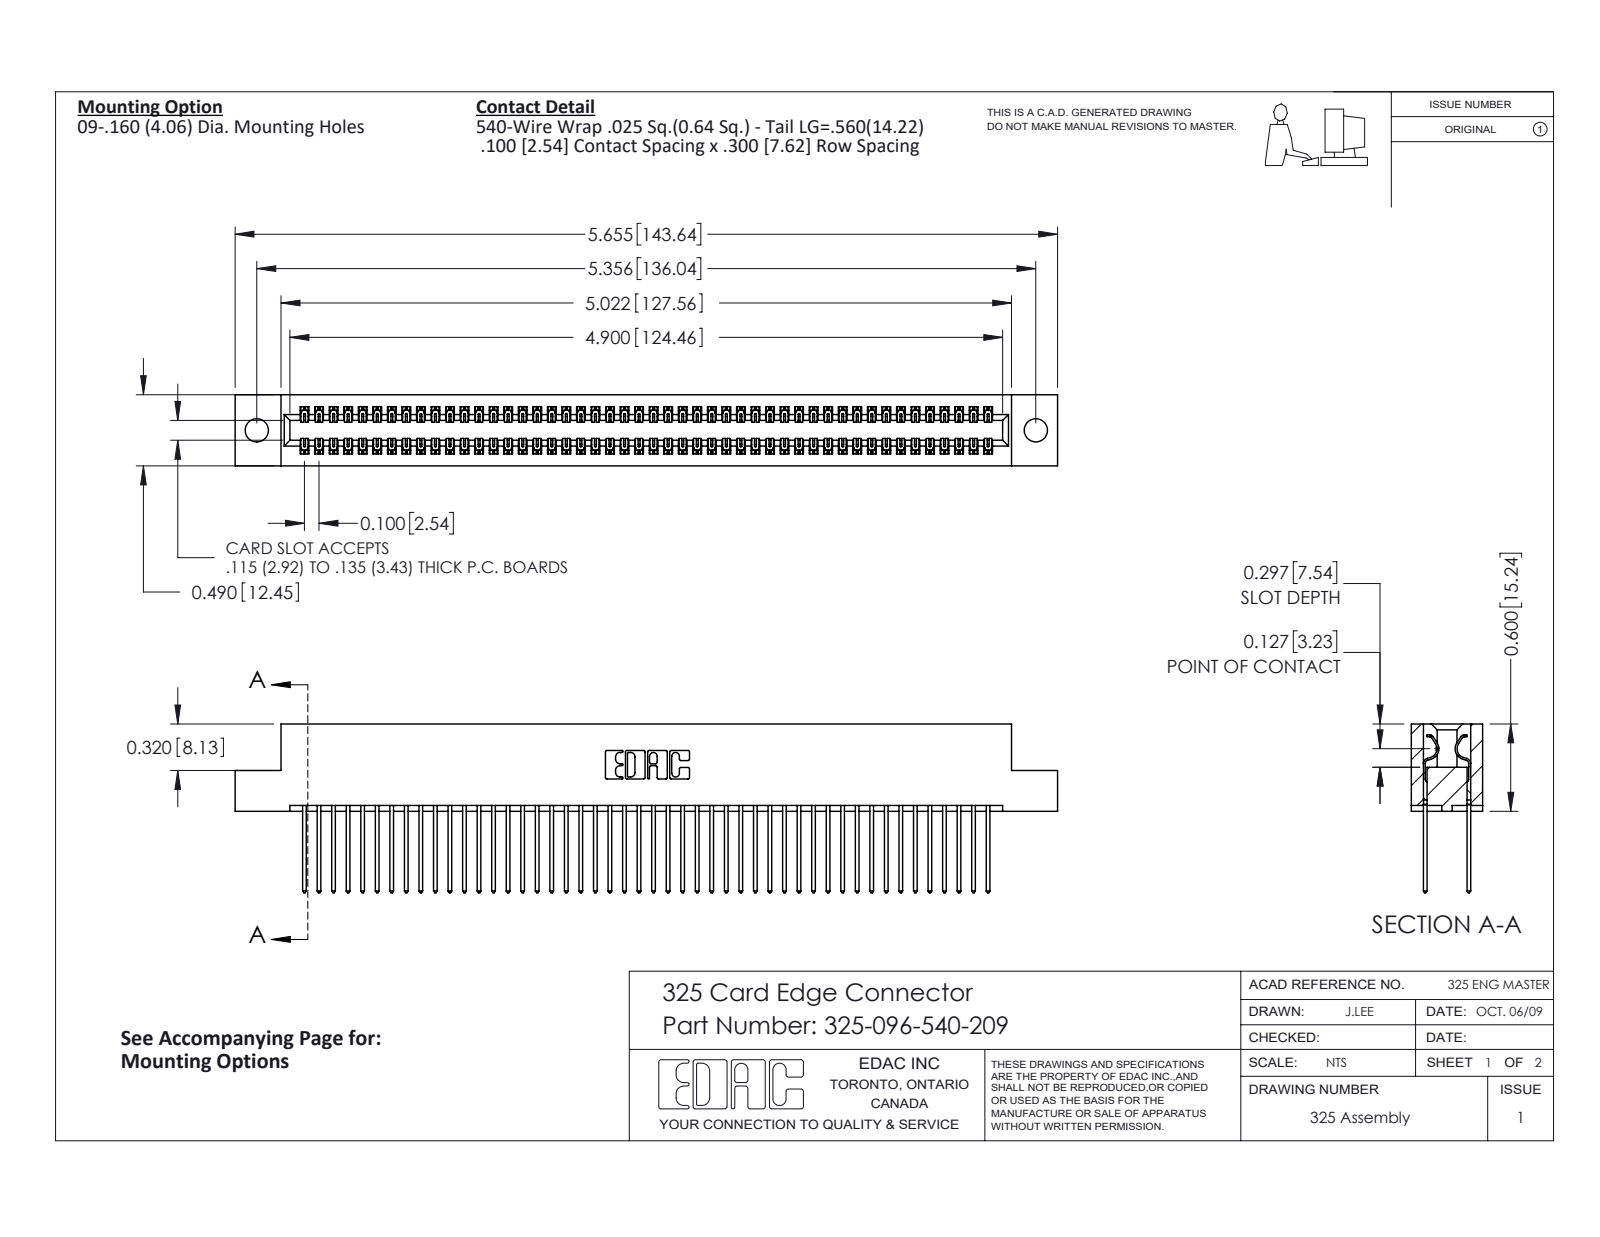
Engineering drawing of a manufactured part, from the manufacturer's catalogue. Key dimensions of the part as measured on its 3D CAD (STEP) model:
Part name (STEP PRODUCT): 325-096-540-209; 325 Part_.160 TH; 325-292-001_325-293-140
STEP written by: SolidWorks 2016 (CONFIG_CONTROL_DESIGN)
Units: inches
Bodies: 97 solids, 5106 faces (3526 planar, 1580 cylindrical, 0 other)
Overall size (bounding box): 5.655 × 1.16 × 0.49
Volume: 1.143 in³ · Surface area: 37.92 in²
Round holes (diameter × count): ⌀0.16 ×2
Partial cylindrical surfaces — rounded edges, fillets, slot ends (radius × count): R0.006 ×144, R0.01 ×96, R0.01 ×22, R0.007 ×6, R0.031 ×6, R0.026 ×3, R0.014 ×2, R0.022 ×2
Main face-to-face distances: 0.083, 0.407, 0.3, 0.107, 0.383, 0.025, 0.325, 0.49, 0.275, 0.56
Hole centre spacings: 5.356
